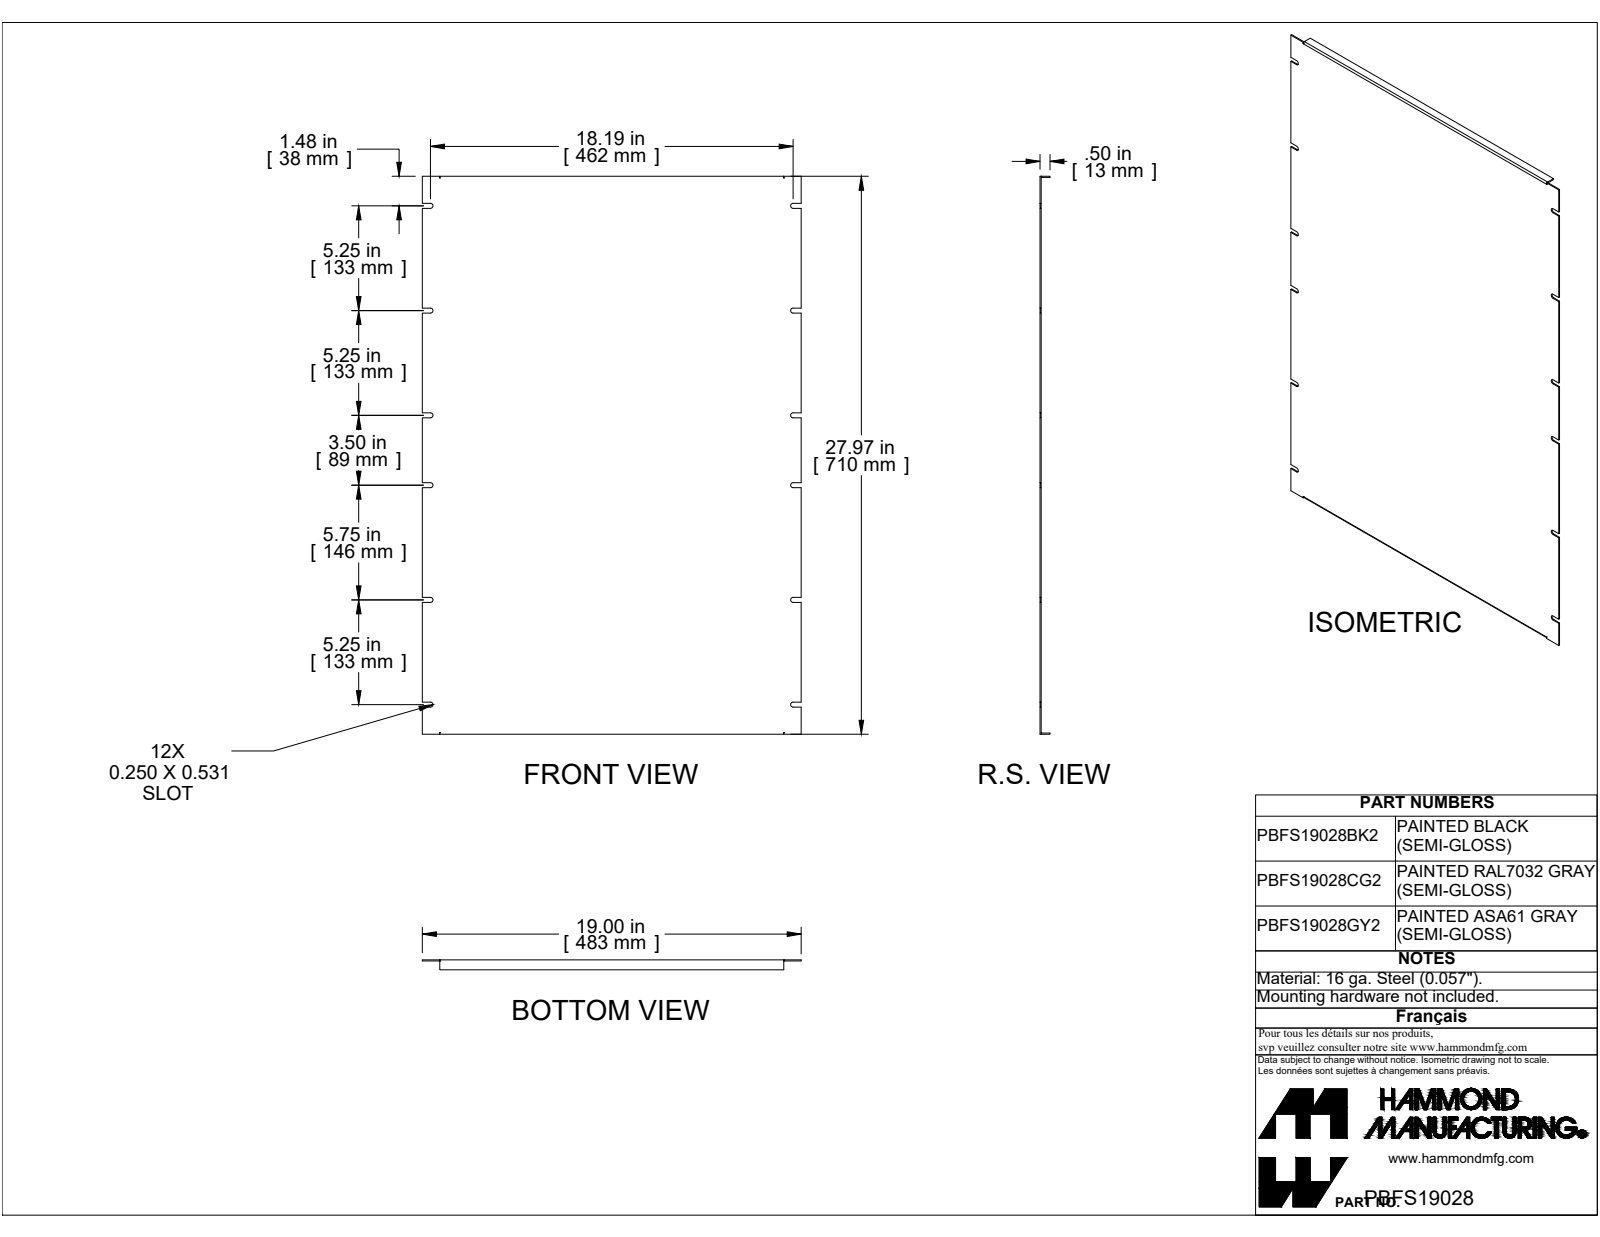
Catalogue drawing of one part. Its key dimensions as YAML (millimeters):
part_name: "PBFS19028"
step_written_by: "SolidWorks 2019 (CONFIG_CONTROL_DESIGN)"
units: millimeters
bodies: {solids: 1, faces: 78, planar: 62, cylindrical: 16, other: 0}
overall_size: [710.4, 482.6, 12.7]
volume: 508500
surface_area: 706500
partial_cylinders:
  - {radius: 3.2, count: 12}
  - {radius: 0.7, count: 2}
  - {radius: 2.2, count: 2}
face_to_face_distances: [1.4, 1.4, 708.9, 710.4, 707.5, 12.7, 11.3, 482.6, 6.4, 133.4]
